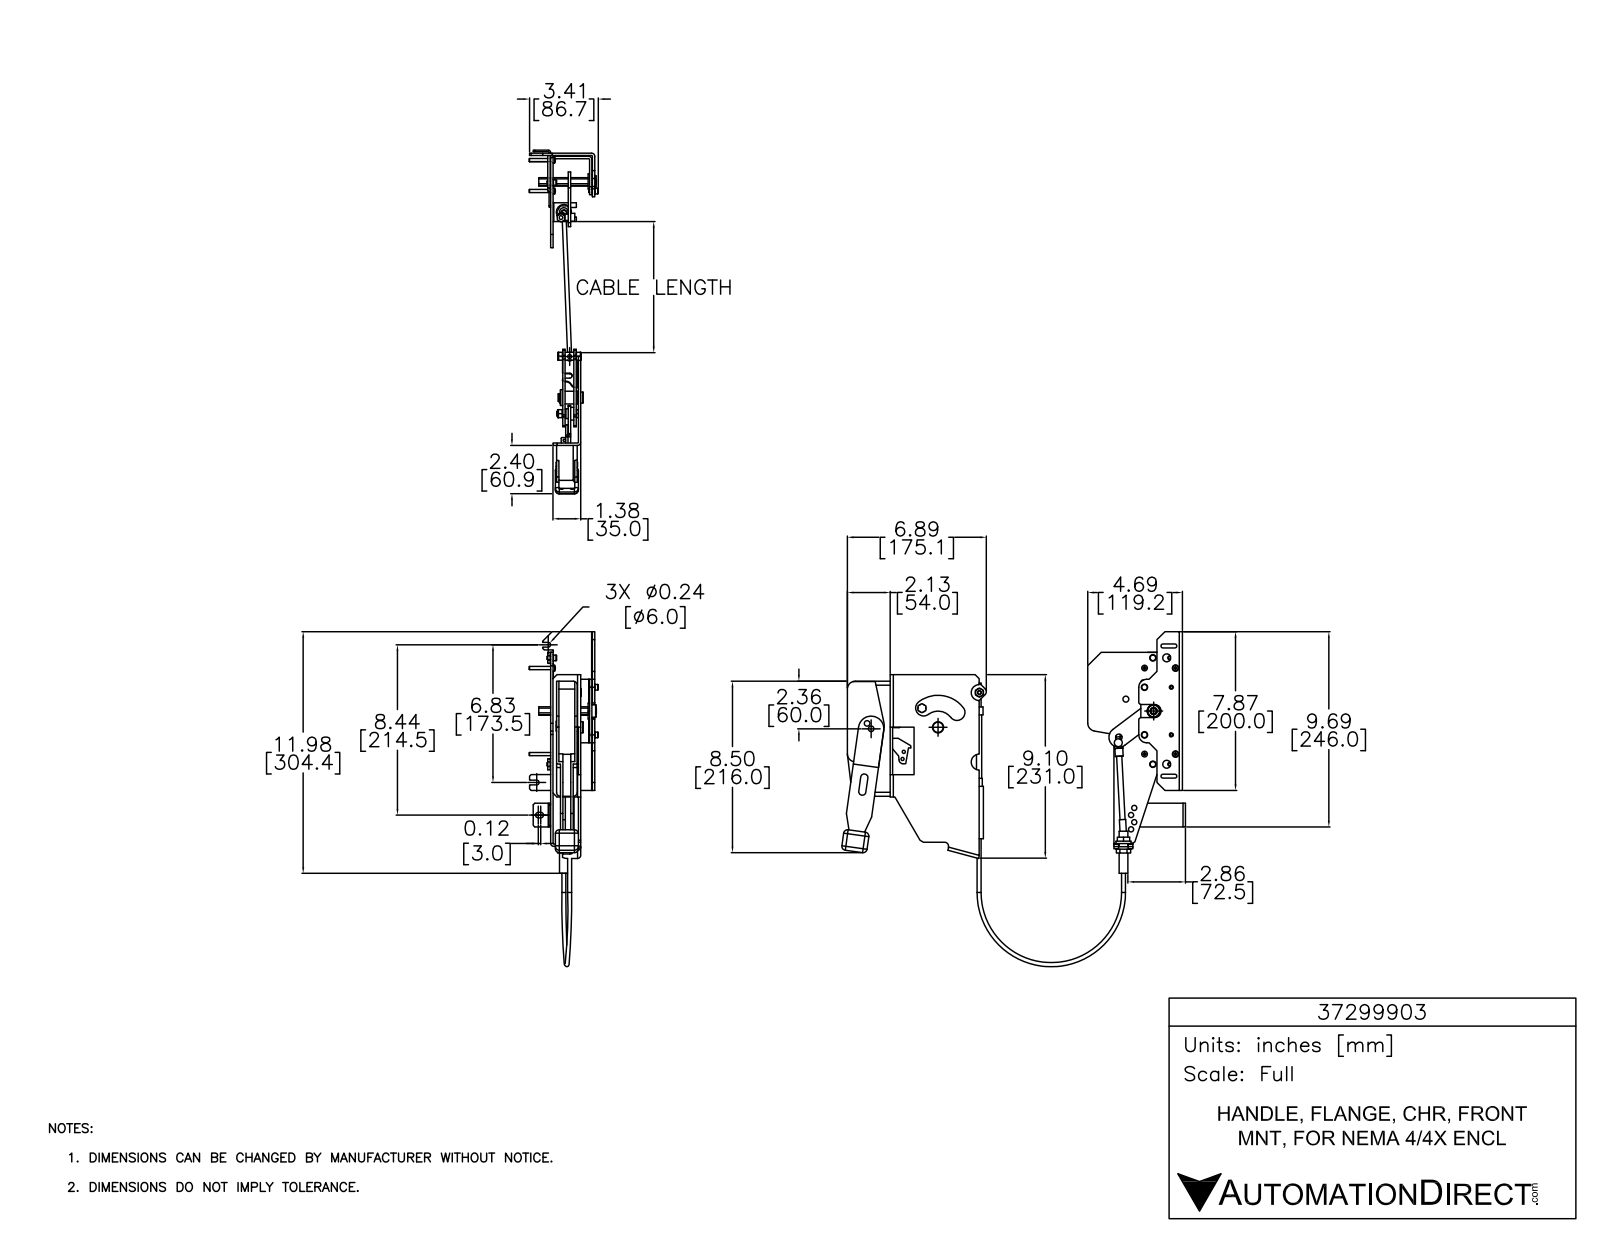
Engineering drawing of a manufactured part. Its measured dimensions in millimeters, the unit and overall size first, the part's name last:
Units: millimetres
Overall size (bounding box): 432.9 × 422 × 87.1
Round holes (diameter × count): ⌀5 ×18, ⌀3.3 ×4, ⌀3.4 ×4, ⌀4.3 ×4, ⌀6.5 ×4, ⌀4 ×2, ⌀5.2 ×2, ⌀7 ×2, ⌀7.1 ×2, ⌀8 ×2, ⌀8.2 ×2, ⌀10 ×2
Round bosses / shafts (diameter × count): ⌀8 ×9, ⌀10 ×6, ⌀7.2 ×4, ⌀7 ×4, ⌀5 ×4, ⌀4 ×4, ⌀3.9 ×4, ⌀20 ×2
Partial cylindrical surfaces — rounded edges, fillets, slot ends (radius × count): R5 ×24, R1 ×19, R10 ×11, R4 ×10, R0.3 ×6, R6 ×5, R0.2 ×4, R2.5 ×4
Main face-to-face distances: 3, 34.9, 37.9, 31.9, 52.6, 17.7, 5, 18, 365.2, 7.4
Hole centre spacings: 3.8, 21.2, 134, 134.1, 135.7, 9.9, 14.5, 16.6
Volume: 490 300 mm³ · Surface area: 267 300 mm²
Bodies: 49 solids, 1007 faces (467 planar, 432 cylindrical, 108 other)
Part name (STEP PRODUCT): 37299003
STEP written by: SolidWorks 2015 (AUTOMOTIVE_DESIGN)
